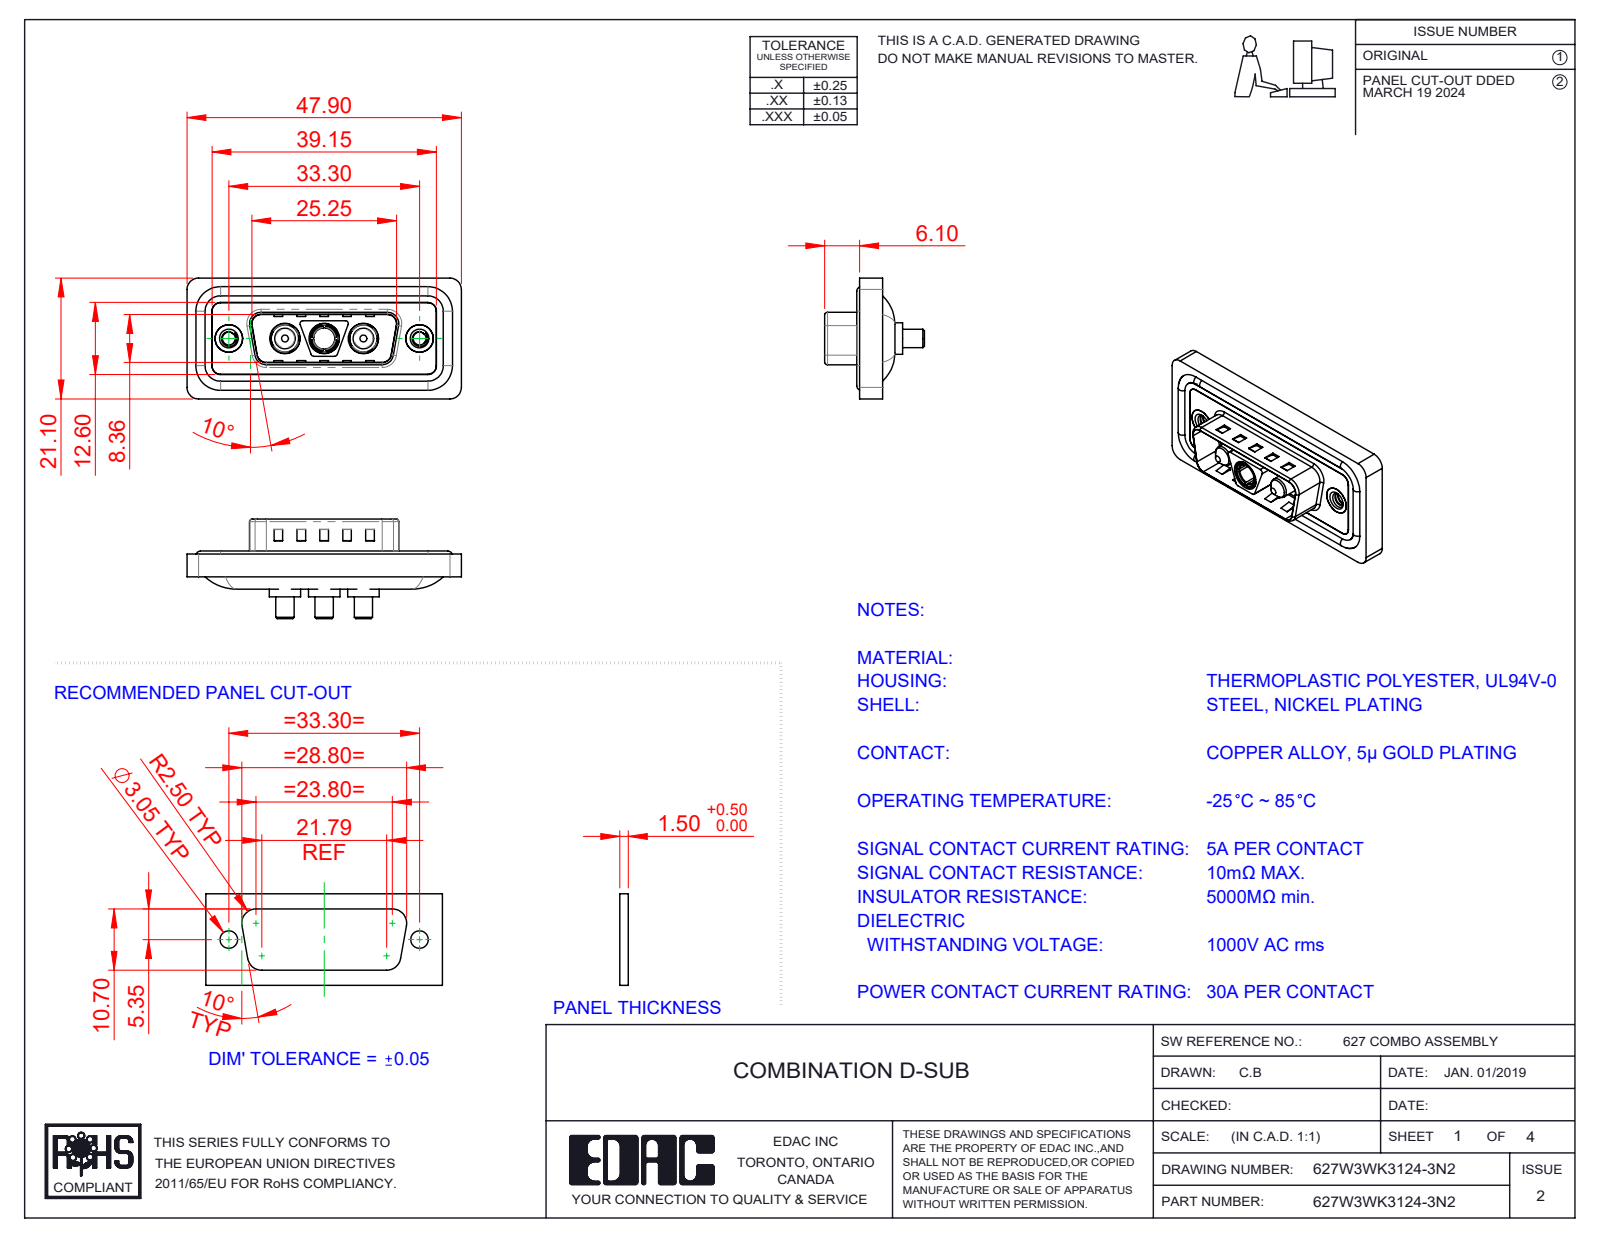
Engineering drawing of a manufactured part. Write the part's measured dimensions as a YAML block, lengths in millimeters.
part_name: "627Combo Housing_3WK3; 627W3WK3124-3N2; 627Combo Threaded Rivet_2; Power Socket_30A S (+4 more)"
step_written_by: "SolidWorks 2023 (CONFIG_CONTROL_DESIGN)"
units: millimeters
bodies: {solids: 13, faces: 609, planar: 231, cylindrical: 250, other: 128}
overall_size: [47.9, 21.1, 17.4]
volume: 5709
surface_area: 9141
round_holes:
  - {diameter: 4.85, count: 3}
  - {diameter: 5.3, count: 3}
  - {diameter: 2.26, count: 2}
  - {diameter: 4, count: 2}
  - {diameter: 4.8, count: 2}
  - {diameter: 5, count: 2}
  - {diameter: 3.7, count: 1}
round_bosses_or_shafts:
  - {diameter: 1.6, count: 4}
  - {diameter: 5.5, count: 3}
  - {diameter: 5.2, count: 3}
  - {diameter: 4.75, count: 3}
  - {diameter: 3.75, count: 3}
  - {diameter: 3.2, count: 3}
  - {diameter: 4.9, count: 2}
  - {diameter: 3.6, count: 2}
partial_cylinders:
  - {radius: 1.5, count: 26}
  - {radius: 2, count: 20}
  - {radius: 0.5, count: 12}
  - {radius: 1.6, count: 8}
  - {radius: 0.25, count: 4}
  - {radius: 0.6, count: 4}
  - {radius: 0.65, count: 4}
  - {radius: 0.9, count: 4}
face_to_face_distances: [0.4, 1.1, 1.5, 0.5, 1.6, 3.1, 2.9, 4, 0.82, 9.58]
hole_center_spacings: [6.85, 9.8, 16.65, 23.5, 13.7, 33.3]
